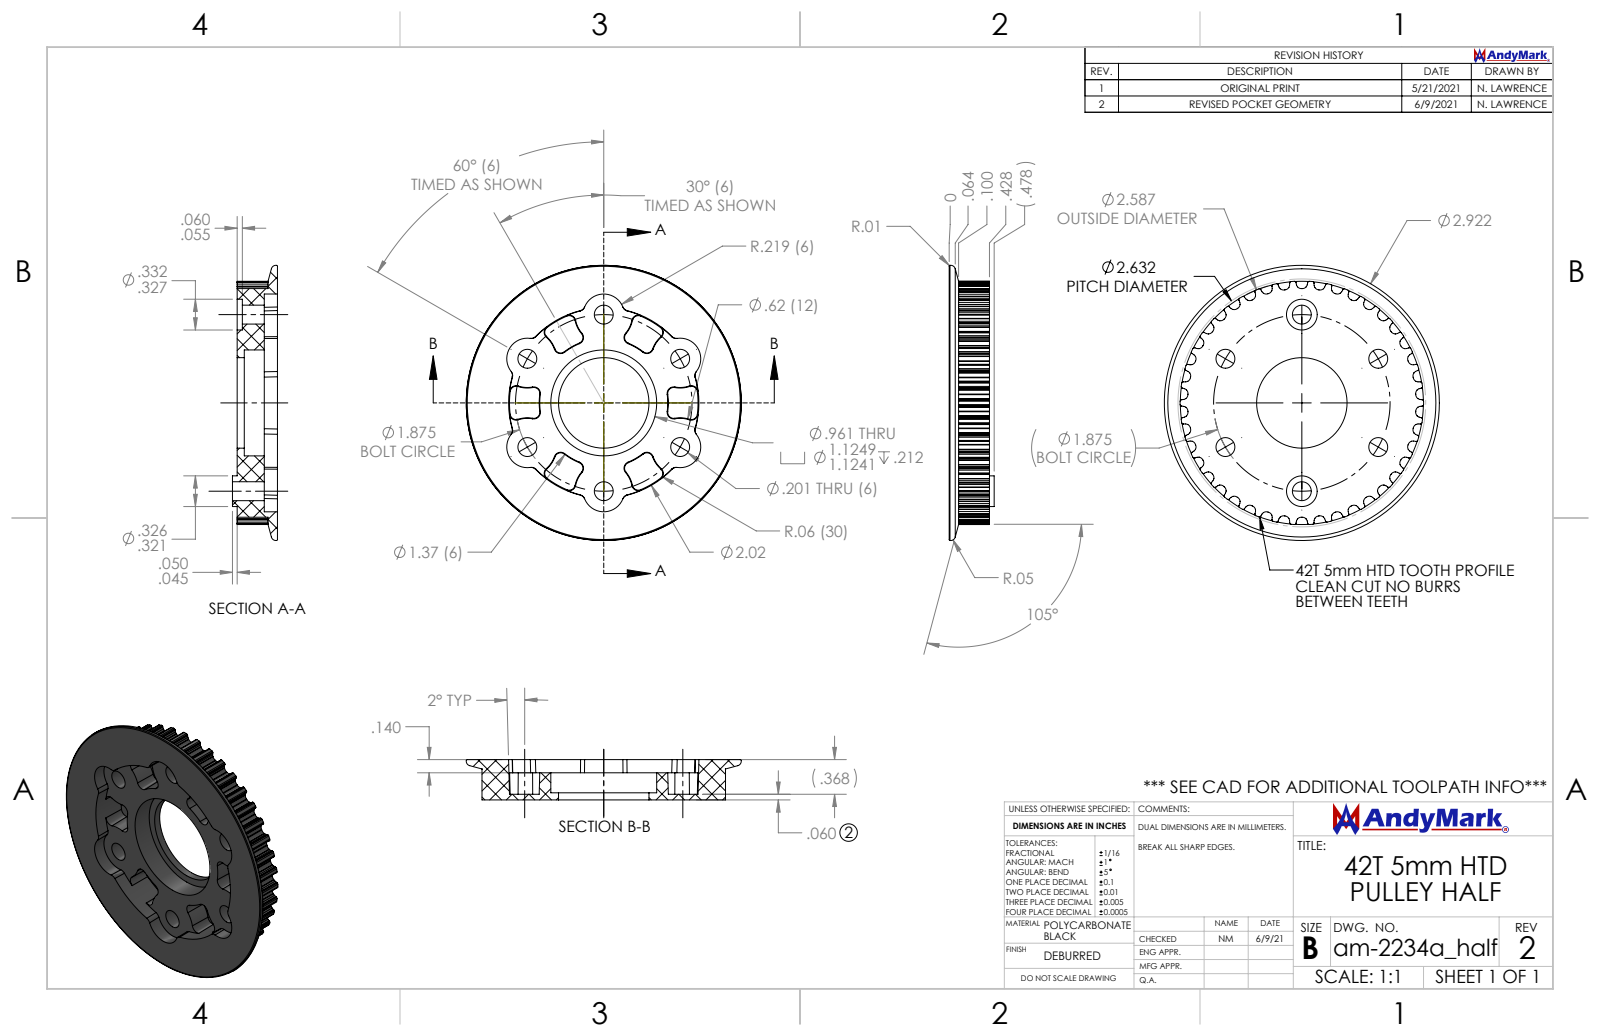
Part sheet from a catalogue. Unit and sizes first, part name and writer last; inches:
Units: inches
Overall size (bounding box): 2.922 × 2.922 × 0.478
Round holes (diameter × count): ⌀0.201 ×6, ⌀0.327 ×1, ⌀0.961 ×1, ⌀1.125 ×1
Round bosses / shafts (diameter × count): ⌀0.326 ×1
Partial cylindrical surfaces — rounded edges, fillets, slot ends (radius × count): R0.015 ×84, R0.017 ×84, R0.029 ×84, R0.054 ×84, R0.069 ×84, R0.089 ×84, R0.112 ×84, R0.219 ×6
Main face-to-face distances: 0.428, 0.14, 0.288, 0.368, 0.228, 0.06, 0.1, 0.04, 0.268, 0.328
Hole centre spacings: 0.937, 1.624, 1.875, 0.938
Volume: 1.289 in³ · Surface area: 20.7 in²
Bodies: 1 solid, 847 faces (138 planar, 646 cylindrical, 63 other)
Part name (STEP PRODUCT): am-2234a_half 42 tooth HTD Pulley half
STEP written by: SolidWorks 2019 (AUTOMOTIVE_DESIGN)
